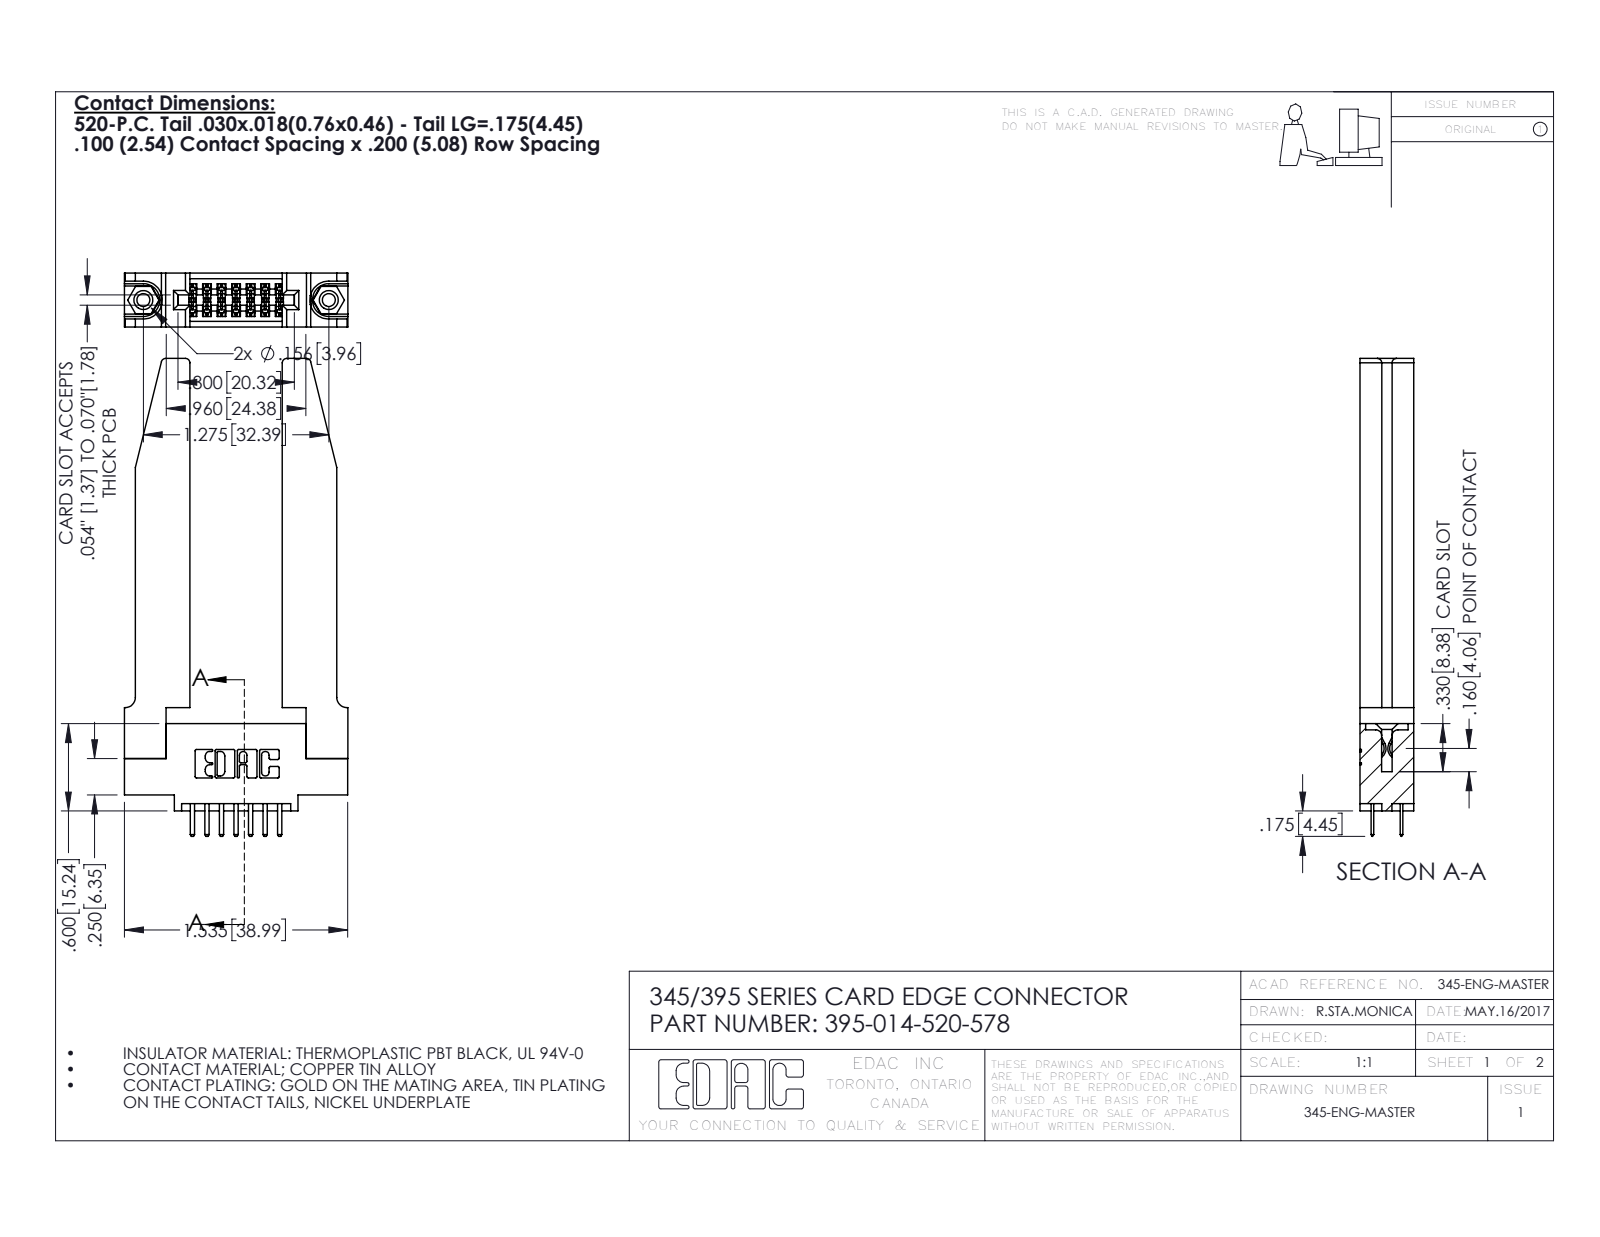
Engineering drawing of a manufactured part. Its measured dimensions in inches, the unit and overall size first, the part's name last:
Units: inches
Overall size (bounding box): 3.285 × 1.536 × 0.37
Round holes (diameter × count): ⌀0.089 ×2, ⌀0.125 ×2, ⌀0.156 ×2, ⌀0.064 ×1
Round bosses / shafts (diameter × count): ⌀0.155 ×2
Partial cylindrical surfaces — rounded edges, fillets, slot ends (radius × count): R0.01 ×22, R0.006 ×21, R0.01 ×18, R0.03 ×8, R0.007 ×6, R0.031 ×6, R0.026 ×3, R0.014 ×2
Main face-to-face distances: 0.37, 0.15, 0.22, 0.072, 0.298, 0.077, 0.148, 0.635, 0.2, 0.055
Hole centre spacings: 0.27, 1.045, 1.275
Volume: 0.681 in³ · Surface area: 17.43 in²
Bodies: 19 solids, 1120 faces (716 planar, 352 cylindrical, 52 other)
Part name (STEP PRODUCT): 345-292-001_345-293-120; 395-014-520-578; 345 Part_0.110 Offset - 0.156 Dia-TH; 345-250-001_345-250-001-102 (+1 more)
STEP written by: SolidWorks 2016 (CONFIG_CONTROL_DESIGN)
